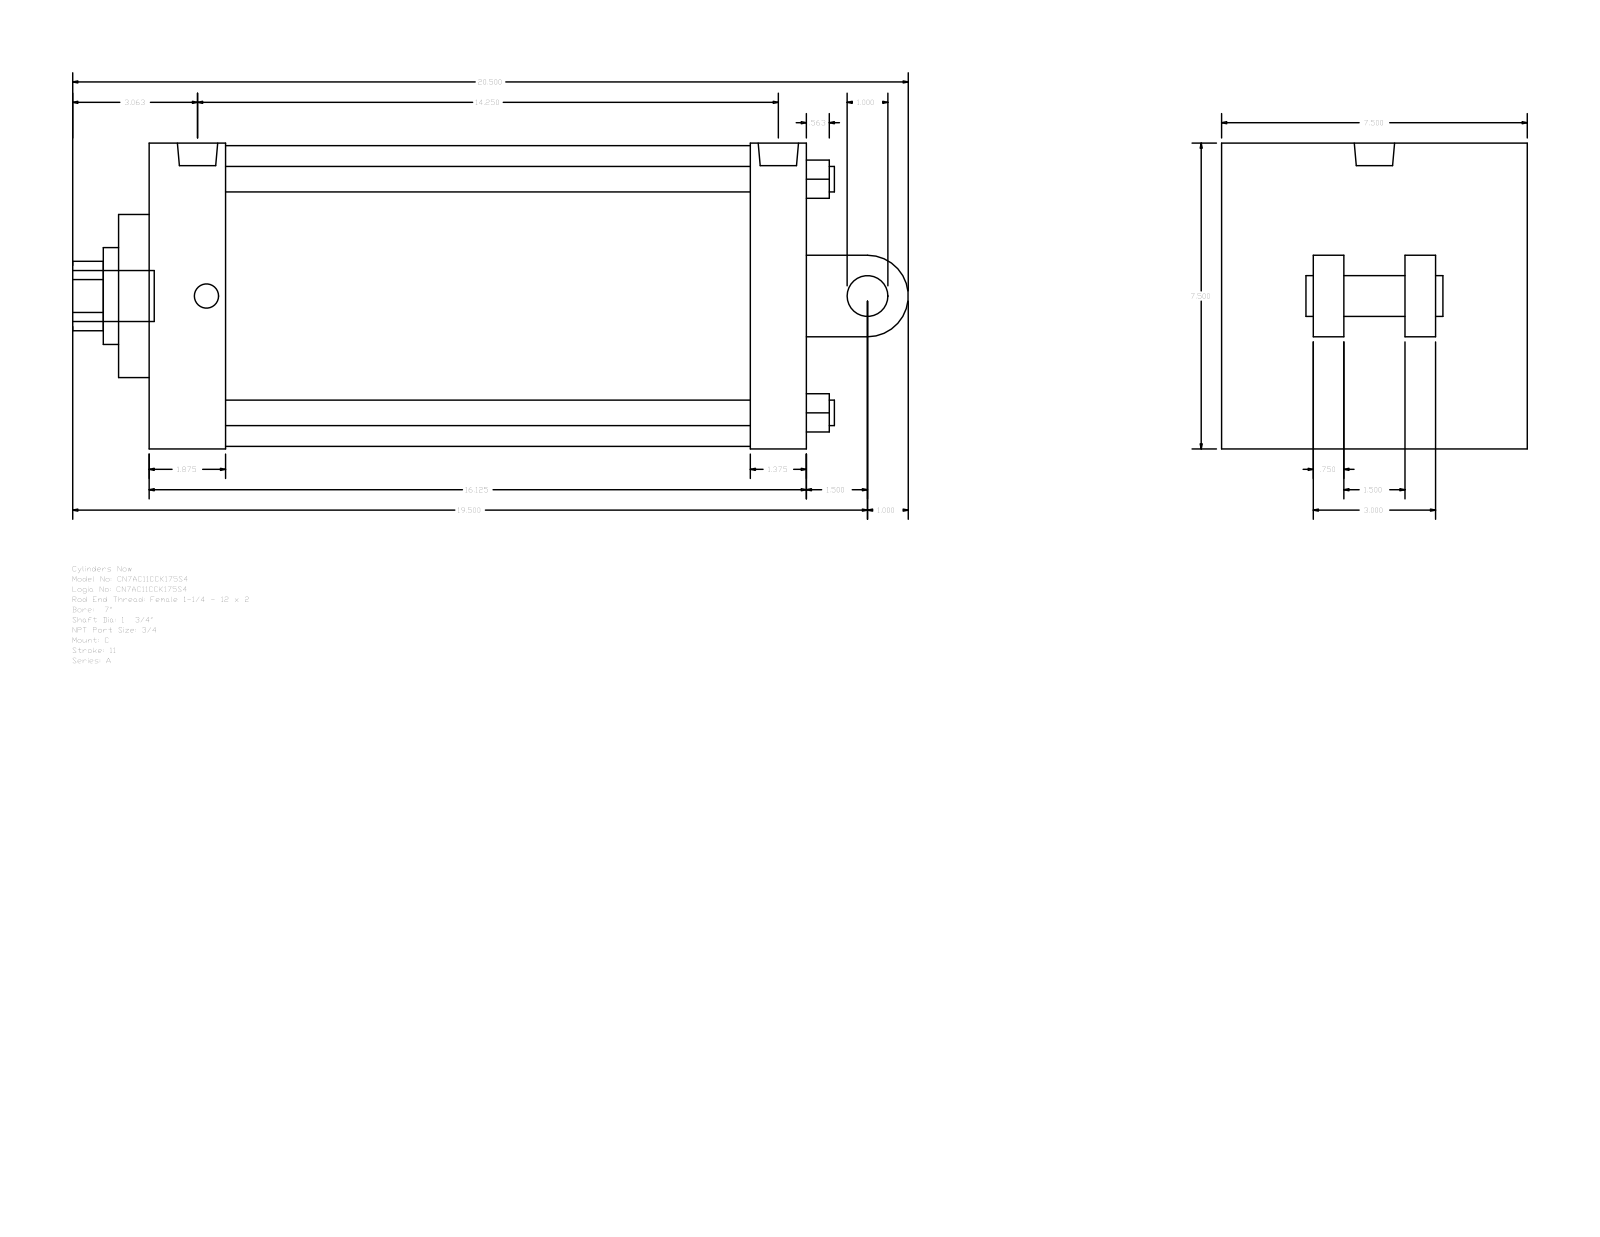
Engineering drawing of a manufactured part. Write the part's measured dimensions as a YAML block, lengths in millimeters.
part_name: "A_C__0700_1.75"
step_written_by: "GSSL Pune (CONFIG_CONTROL_DESIGN)"
units: millimeters
bodies: {solids: 0, faces: 104, planar: 75, cylindrical: 29, other: 0}
overall_size: [520.7, 190.5, 190.5]
round_holes:
  - {diameter: 15.88, count: 4}
  - {diameter: 15.08, count: 2}
  - {diameter: 25.12, count: 1}
  - {diameter: 44.45, count: 1}
  - {diameter: 60.33, count: 1}
  - {diameter: 187.32, count: 1}
round_bosses_or_shafts:
  - {diameter: 15.08, count: 2}
  - {diameter: 31.75, count: 1}
  - {diameter: 25.4, count: 1}
  - {diameter: 25.12, count: 1}
partial_cylinders:
  - {radius: 21.63, count: 1}
  - {radius: 25.4, count: 1}
face_to_face_distances: [190.5, 409.58, 19.05, 76.2, 57.15, 44.45, 47.63, 361.95, 374.65, 327.02]
hole_center_spacings: [102.91, 145.54, 205.82, 5.56]
